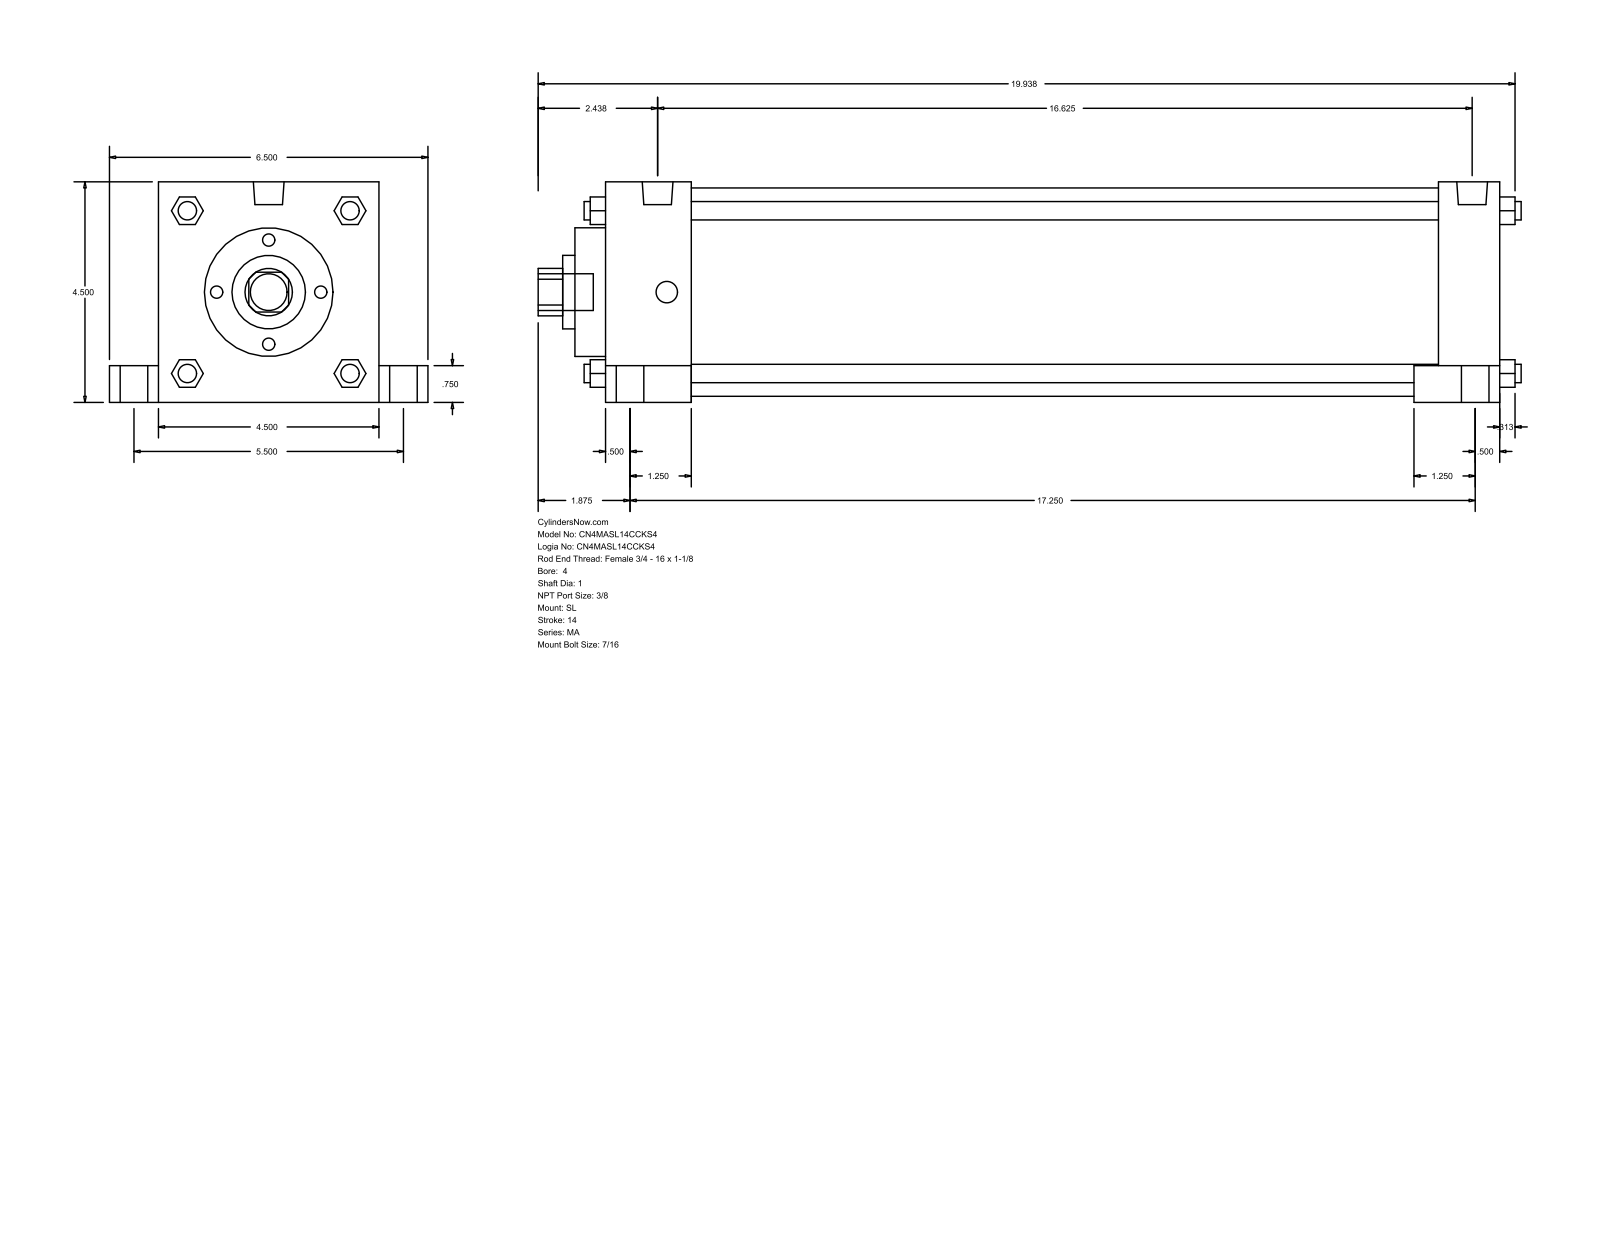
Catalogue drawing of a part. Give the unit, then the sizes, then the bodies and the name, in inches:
Units: inches
Overall size (bounding box): 20.063 × 6.5 × 4.5
Round holes (diameter × count): ⌀1 ×1, ⌀1.5 ×1, ⌀2.625 ×1, ⌀4.25 ×1
Round bosses / shafts (diameter × count): ⌀0.813 ×4, ⌀0.563 ×4, ⌀0.437 ×4, ⌀0.375 ×4, ⌀0.627 ×2, ⌀0.75 ×1
Partial cylindrical surfaces — rounded edges, fillets, slot ends (radius × count): R0.484 ×1
Main face-to-face distances: 4.5, 18.25, 15.25, 1.75, 16.5, 17, 1.25, 1, 5.5, 0.75
Bodies: 0 solids, 150 faces (113 planar, 37 cylindrical, 0 other)
Part name (STEP PRODUCT): MA_SL__0400_1
STEP written by: GSSL Pune (CONFIG_CONTROL_DESIGN)
